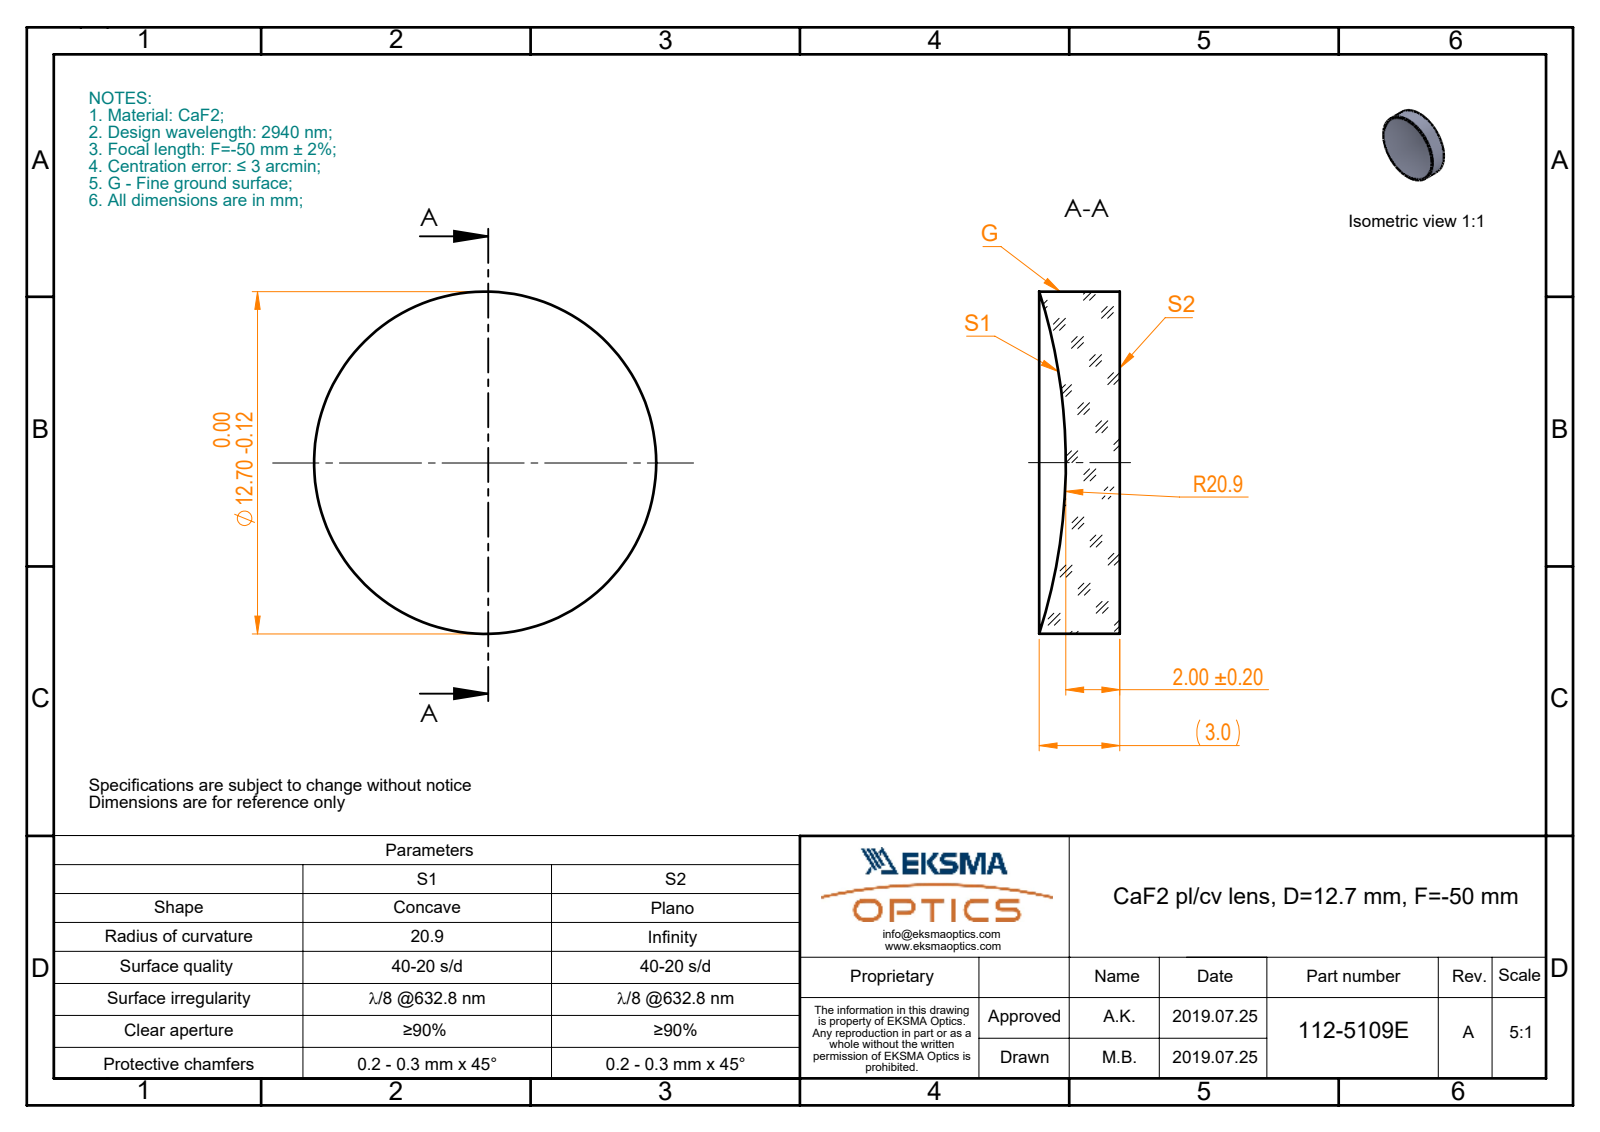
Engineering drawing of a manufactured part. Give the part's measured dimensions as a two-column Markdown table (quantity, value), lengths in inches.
| quantity | value |
| --- | --- |
| part name | 112-5109E CaF2 pl-cv 12.7 F-50 |
| STEP written by | SolidWorks 2017 (CONFIG_CONTROL_DESIGN) |
| units | inches |
| bodies | 1 solid, 5 faces (1 planar, 2 cylindrical, 2 other) |
| overall size | 0.5 × 0.5 × 0.118 |
| volume | 0.019 in³ |
| surface area | 0.583 in² |
| round bosses / shafts (diameter × count) | 0.5 × 1 |
